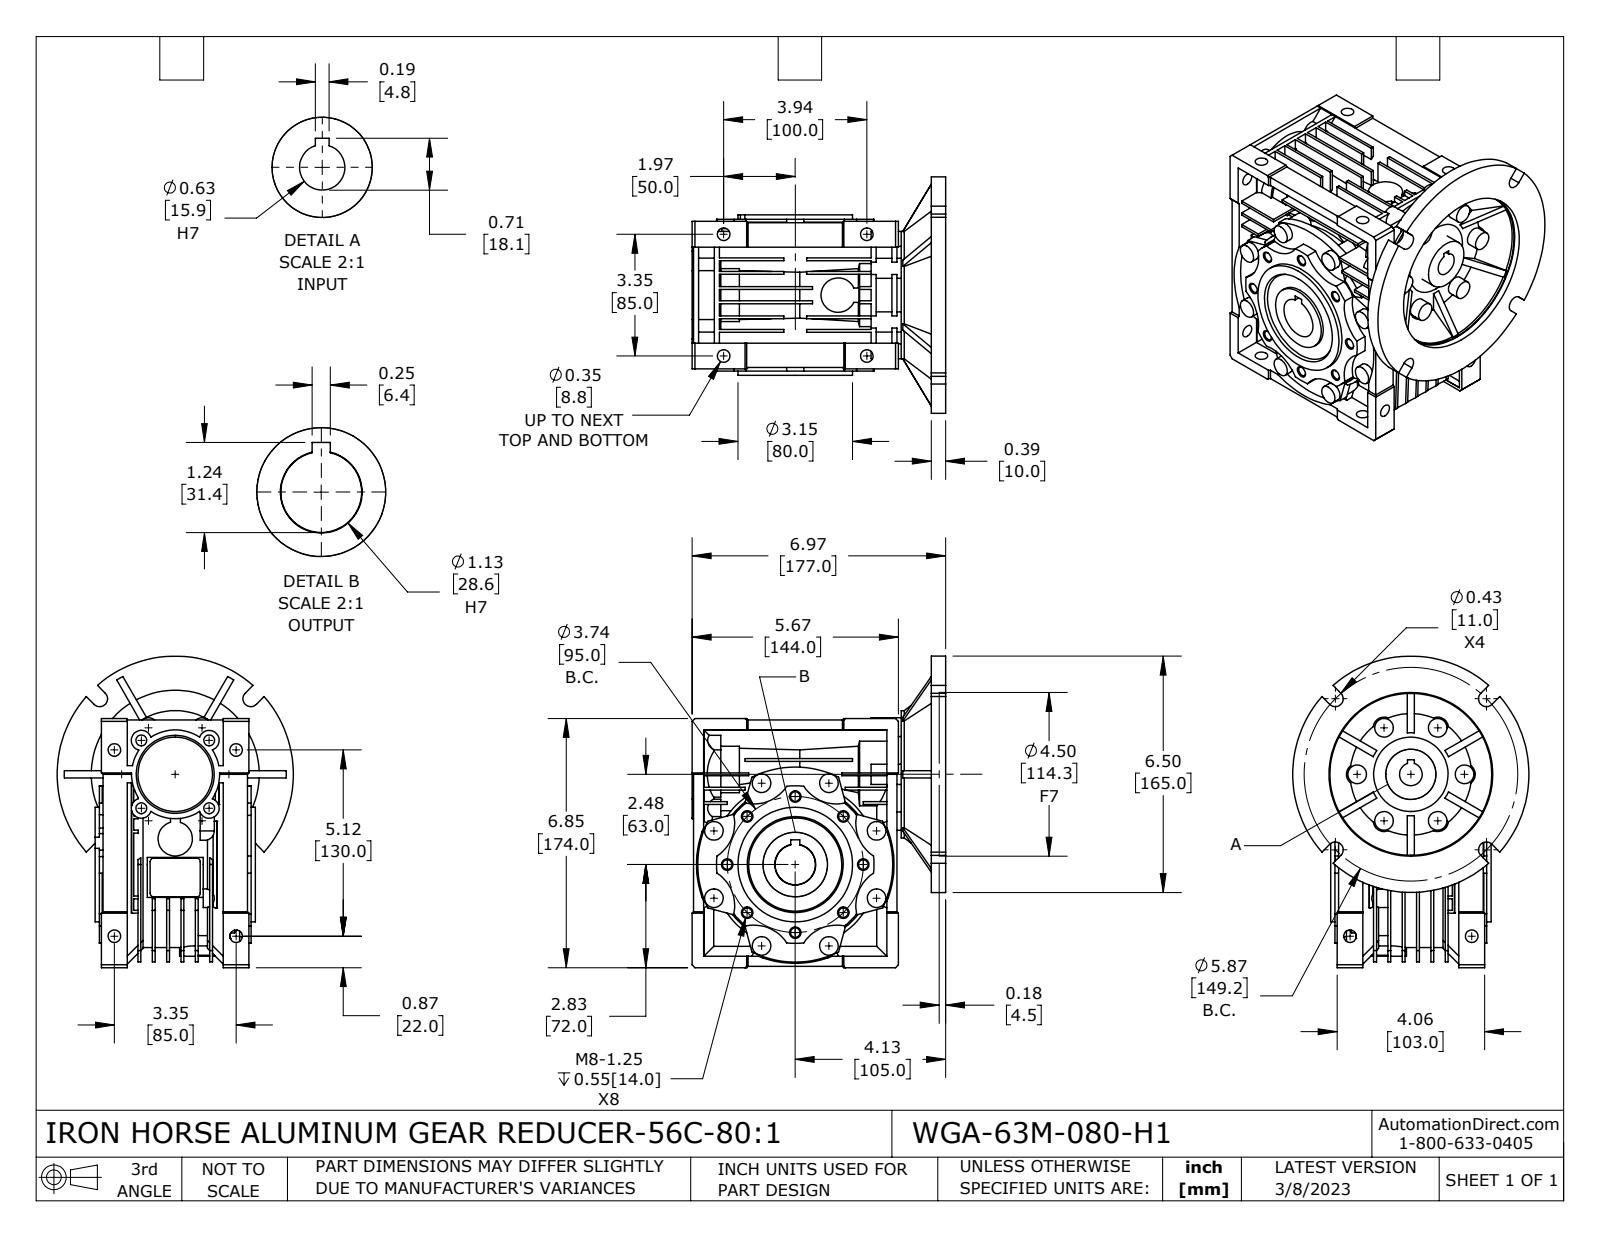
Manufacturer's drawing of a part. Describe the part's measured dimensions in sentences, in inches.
The part is named "WGA-63M-080-H1". Its 3-D file was written by "SolidWorks 2021 (CONFIG_CONTROL_DESIGN)". It is 4 solids with 1231 faces: 759 planar, 331 cylindrical and 141 other. Overall it measures 8.563 by 6.969 by 6.496 inches. Its volume is 117 cubic inches and its surface area 568 square inches. Round holes: 8 of diameter 0.262, 8 of diameter 0.262, 8 of diameter 0.346, 4 of diameter 0.298, 1 of diameter 0.625, 1 of diameter 0.65, 1 of diameter 1.125, 1 of diameter 1.339, 1 of diameter 1.457, 1 of diameter 1.772, 1 of diameter 2.047, 1 of diameter 4.449. Round bosses or shafts: 14 of diameter 0.512, 3 of diameter 0.945, 1 of diameter 6.496, 1 of diameter 4.331, 1 of diameter 3.504, 1 of diameter 3.15, 1 of diameter 2.717, 1 of diameter 2.441. Partial cylindrical surfaces (rounded edges, fillets, slot ends): 10 of radius 0.276, 8 of radius 1.063, 6 of radius 0.295, 4 of radius 0.098, 4 of radius 0.217, 1 of radius 0.329, 1 of radius 1.161, 1 of radius 1.201. The main face-to-face distances are 0.394, 0.315, 0.787, 0.079, 1.181, 0.276, 0.472, 0.709, 1.575, 1.22. The hole center spacings are 1.431, 1.87, 2.645, 3.456, 1.319, 1.865, 3.346, 0.786.
